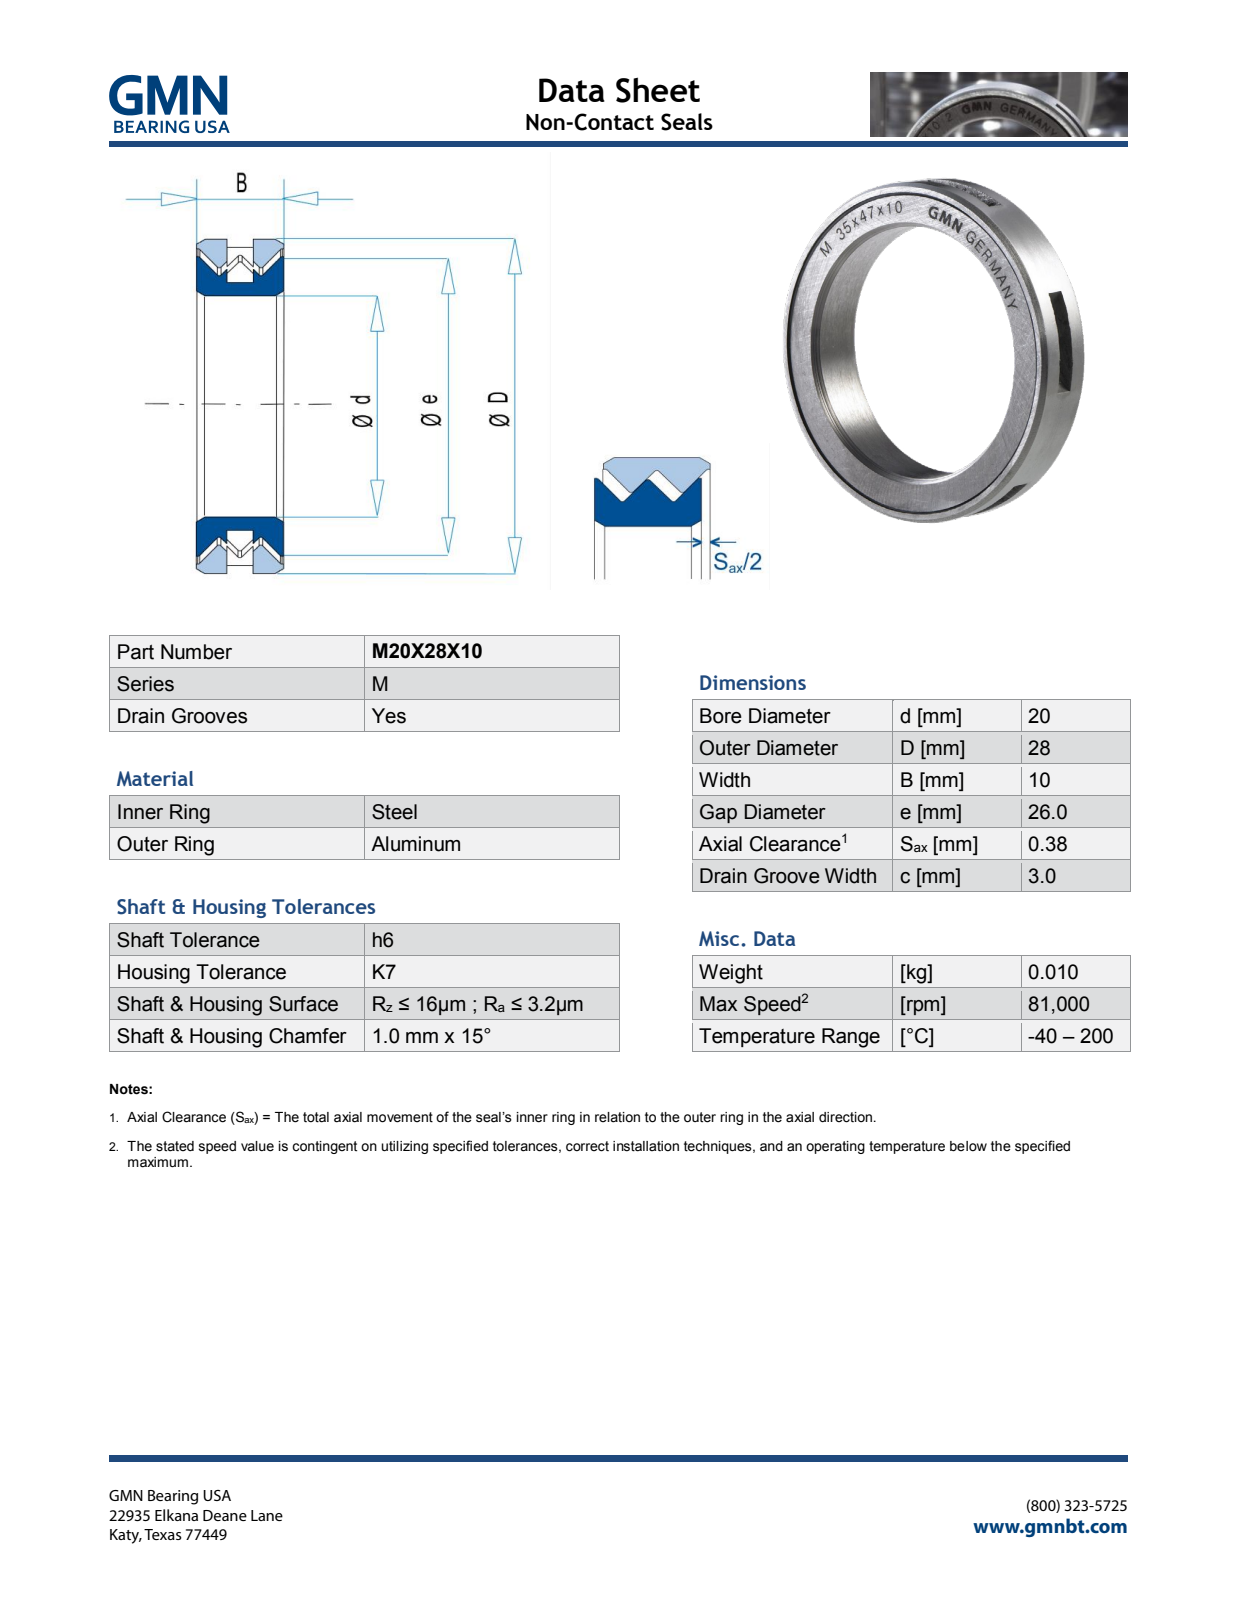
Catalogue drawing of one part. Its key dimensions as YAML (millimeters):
part_name: "M20X28X10_PRT"
step_written_by: "PRO/ENGINEER BY PARAMETRIC TECHNOLOGY CORPORATION, 2013150 (AUTOMOTIVE_DESIGN)"
units: millimeters
bodies: {solids: 2, faces: 624, planar: 557, cylindrical: 21, other: 46}
overall_size: [28, 28, 10.07]
volume: 2644
surface_area: 3936
round_holes:
  - {diameter: 20, count: 1}
  - {diameter: 26.27, count: 1}
round_bosses_or_shafts:
  - {diameter: 28, count: 1}
  - {diameter: 26, count: 1}
partial_cylinders:
  - {radius: 10, count: 3}
face_to_face_distances: [10, 3.5, 6.5, 3, 3.57, 6.57, 10.07, 0.37, 0.43, 0.42]
